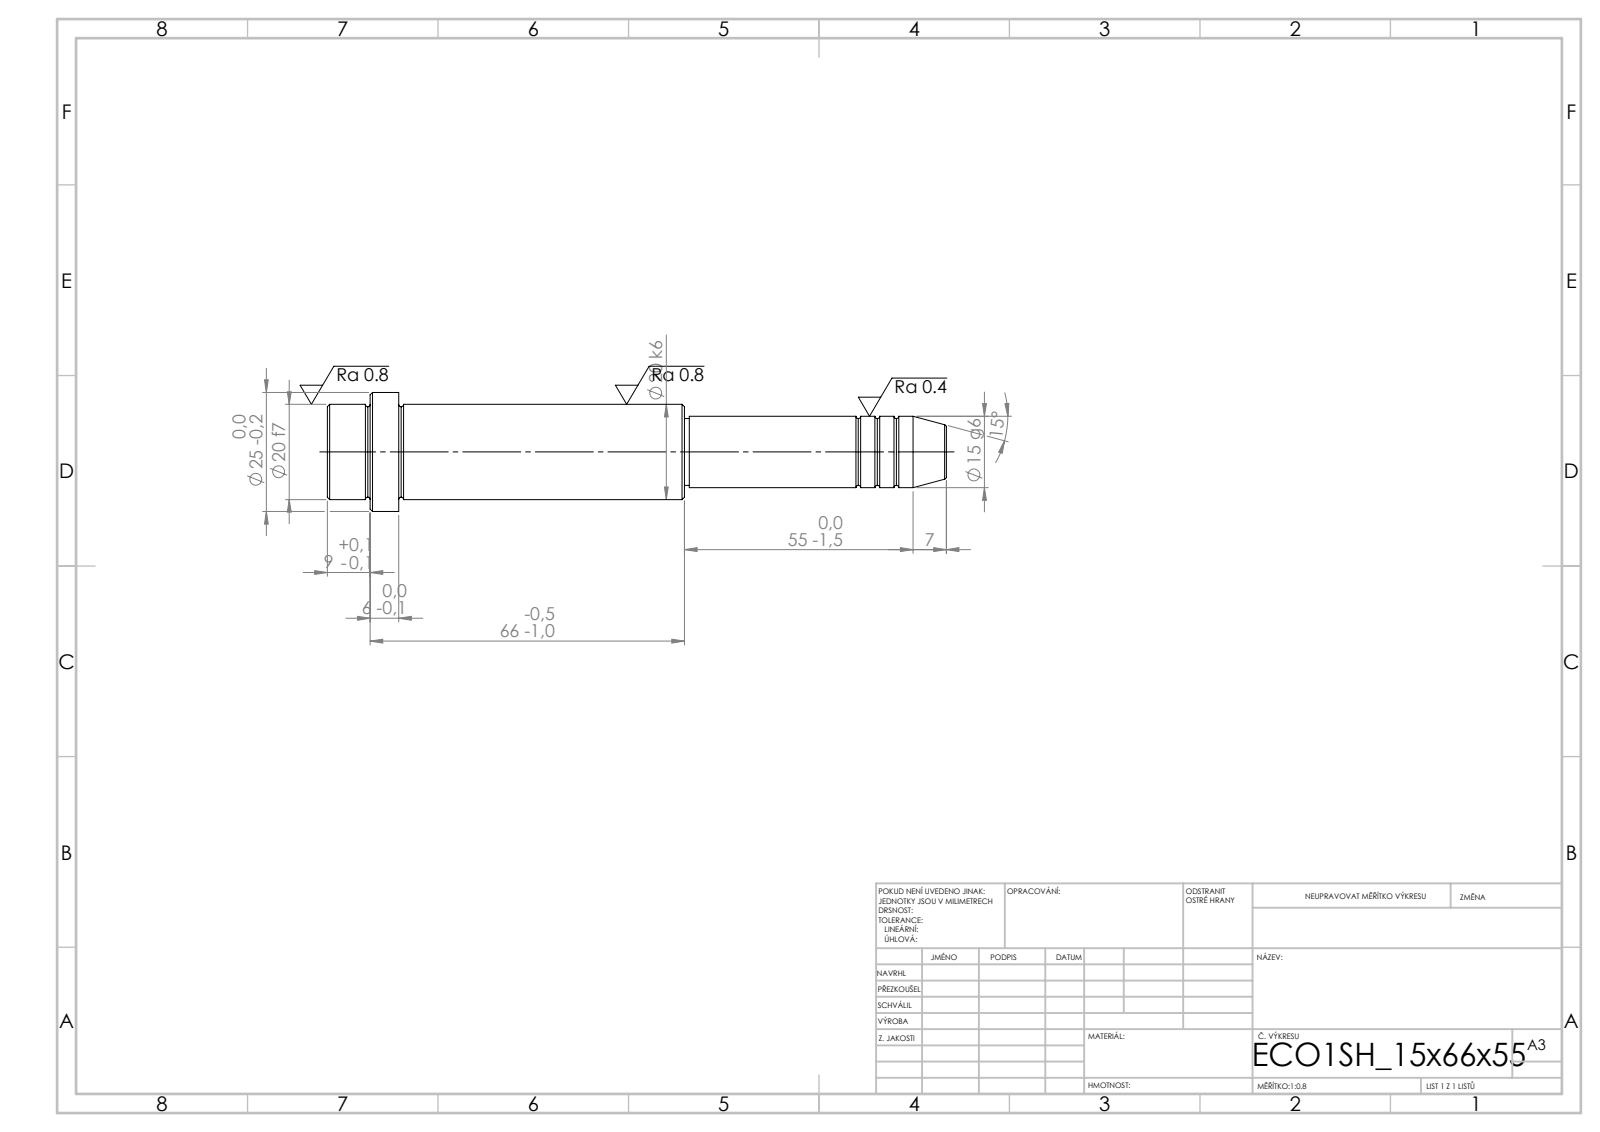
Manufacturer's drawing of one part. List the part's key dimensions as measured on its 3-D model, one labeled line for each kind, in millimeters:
STEP written by: SolidWorks 2019 (CONFIG_CONTROL_DESIGN)
Units: millimetres
Bodies: 1 solid, 52 faces (6 planar, 16 cylindrical, 30 other)
Overall size (bounding box): 130 × 25 × 25
Volume: 33 907 mm³ · Surface area: 8 386 mm²
Round bosses / shafts (diameter × count): ⌀25 ×1, ⌀20 ×1, ⌀15 ×1, ⌀14 ×1
Main face-to-face distances: 15, 6, 9, 60, 66, 75, 55, 115, 121, 130
